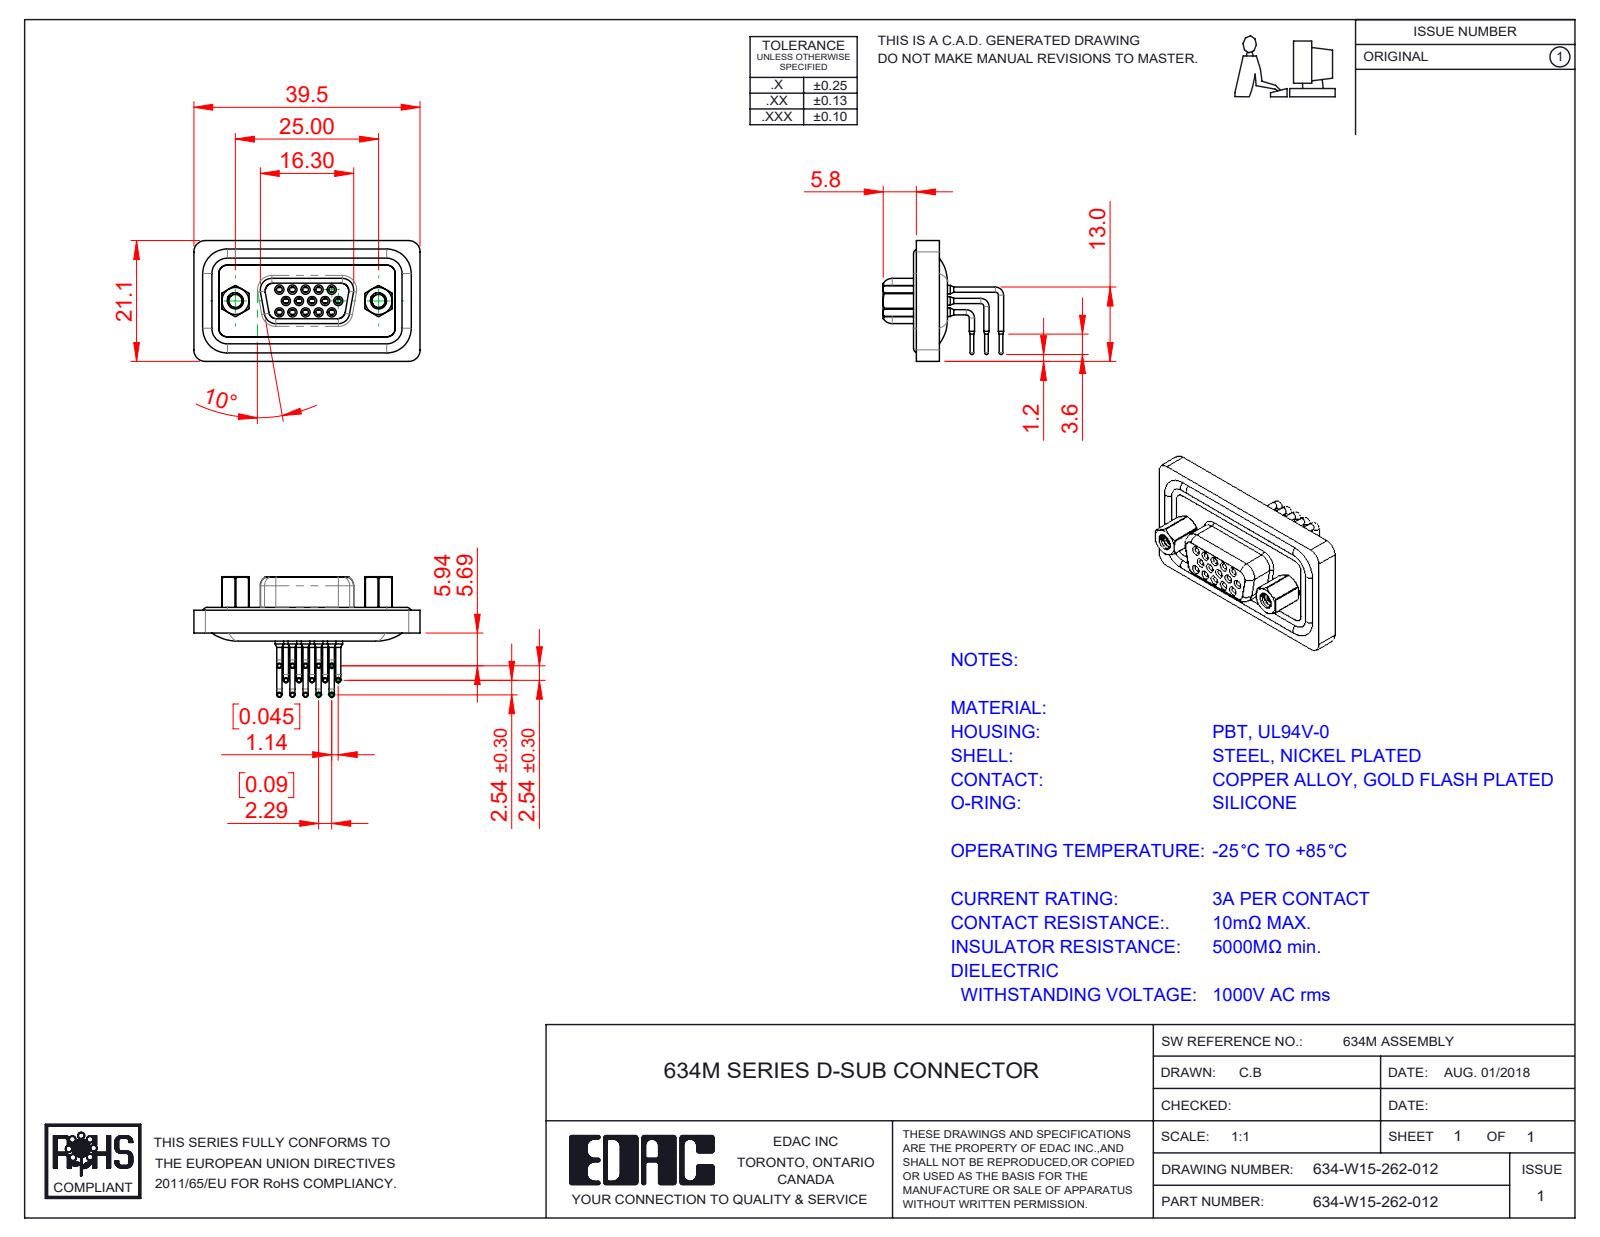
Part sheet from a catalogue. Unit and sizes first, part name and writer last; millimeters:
Units: millimetres
Overall size (bounding box): 39.51 × 21.1 × 21.07
Round holes (diameter × count): ⌀1 ×15, ⌀1.1 ×15, ⌀1.5 ×15, ⌀1.7 ×15, ⌀1.8 ×15, ⌀2 ×15, ⌀2.26 ×2, ⌀2.29 ×2, ⌀4 ×2, ⌀4.8 ×2, ⌀5 ×2
Round bosses / shafts (diameter × count): ⌀0.9 ×30, ⌀1.6 ×19, ⌀0.65 ×15, ⌀1.5 ×6, ⌀4.9 ×2, ⌀2.79 ×2, ⌀5 ×1
Partial cylindrical surfaces — rounded edges, fillets, slot ends (radius × count): R1.5 ×14, R2 ×14, R1.35 ×8, R2.7 ×6, R0.5 ×4, R0.9 ×4, R1.6 ×4, R1.75 ×4
Main face-to-face distances: 0.4, 1.6, 1.8, 1.1, 2.9, 2.5, 0.5, 3.6, 4, 0.7
Hole centre spacings: 2.28, 3.96, 2.29, 4.57, 6.05, 6.04, 3.95, 8.24
Volume: 4 428 mm³ · Surface area: 8 446 mm²
Bodies: 23 solids, 1246 faces (326 planar, 591 cylindrical, 329 other)
Part name (STEP PRODUCT): 634W Housing_15 Contacts; 634-W15-262-012; 634W 4-40 Threaded Rivet; 634W Waterproof Housing_15 Contacts (+5 more)
STEP written by: SolidWorks 2016 (CONFIG_CONTROL_DESIGN)
